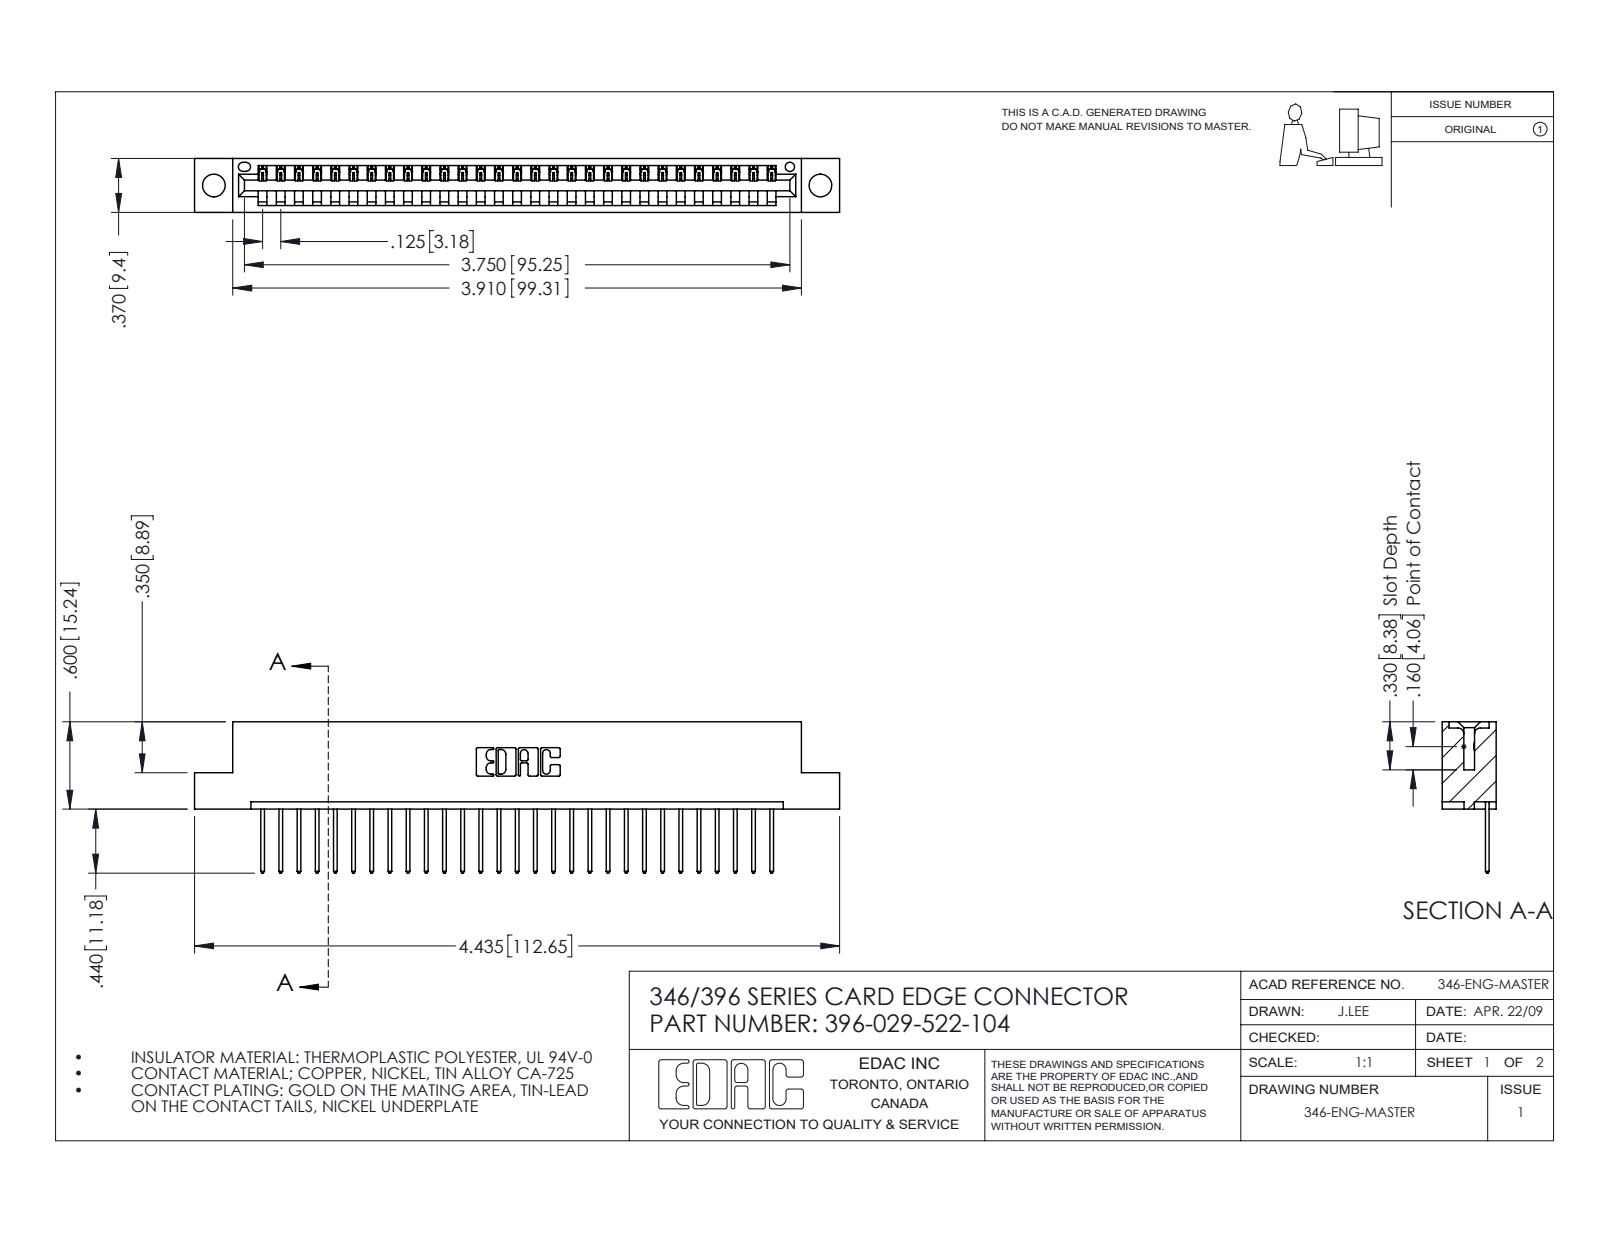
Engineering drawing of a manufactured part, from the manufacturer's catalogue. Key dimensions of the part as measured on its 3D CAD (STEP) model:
Part name (STEP PRODUCT): 345-292-001_345-293-122; 396-029-522-104; 346 Part_Flush Mounting Lugs - 0.156 Dia-TH
STEP written by: SolidWorks 2016 (CONFIG_CONTROL_DESIGN)
Units: inches
Bodies: 30 solids, 1804 faces (1236 planar, 568 cylindrical, 0 other)
Overall size (bounding box): 4.435 × 1.04 × 0.37
Volume: 0.647 in³ · Surface area: 20.2 in²
Round holes (diameter × count): ⌀0.156 ×2, ⌀0.064 ×1
Partial cylindrical surfaces — rounded edges, fillets, slot ends (radius × count): R0.006 ×58, R0.01 ×58, R0.01 ×22, R0.007 ×6, R0.031 ×6, R0.026 ×3, R0.031 ×2, R0.04 ×2
Main face-to-face distances: 0.048, 0.322, 0.37, 0.25, 0.072, 0.298, 0.025, 0.148, 0.222, 0.1
Hole centre spacings: 0.246, 3.962, 4.17
